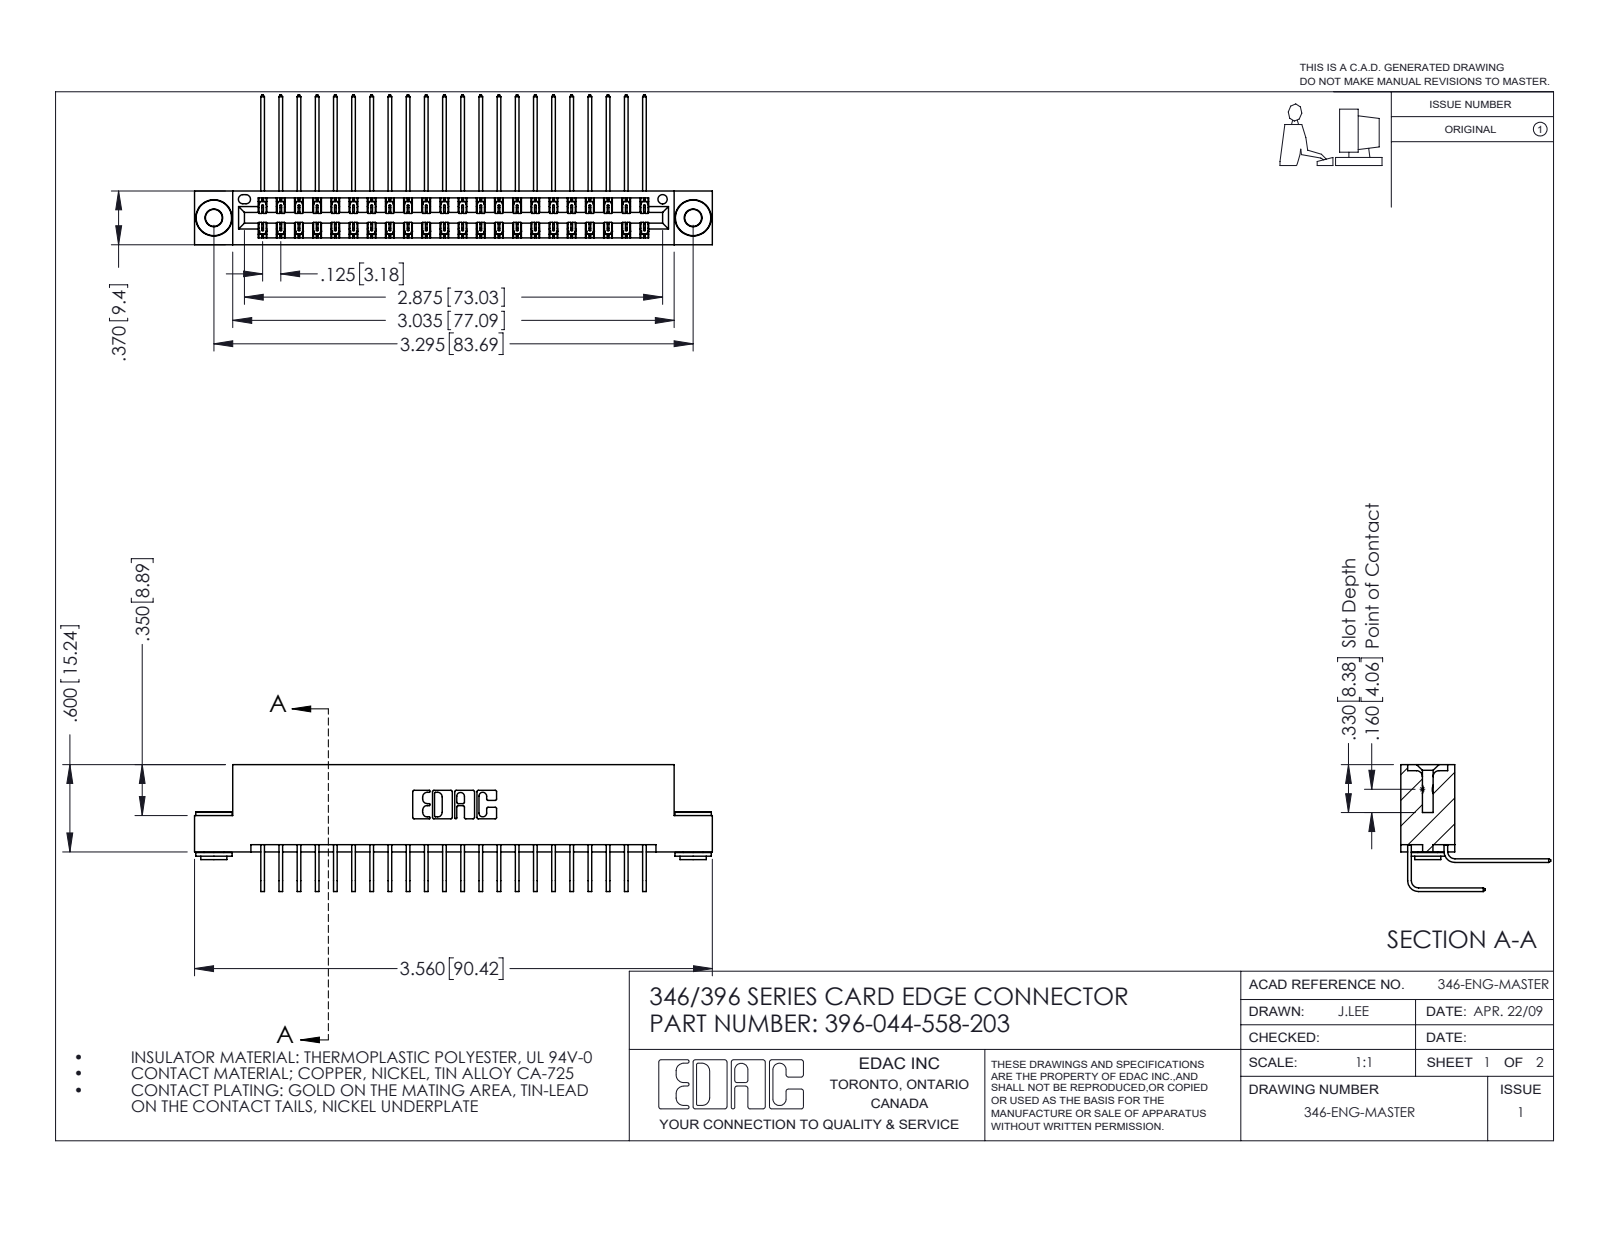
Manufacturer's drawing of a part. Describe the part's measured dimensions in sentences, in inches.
The part is named "345-250-002_345-250-002-102; 346 Part_Flush Mounting Lugs - 0.156 Dia-TH; 396-044-558-203; 345-292-001_558 Tail - 2 (+1 more)". Its 3-D file was written by "SolidWorks 2016 (CONFIG_CONTROL_DESIGN)". It is 47 solids with 2536 faces: 1714 planar, 814 cylindrical and 8 other. Overall it measures 3.56 by 1.03 by 0.873 inches. Its volume is 0.545 cubic inches and its surface area 20.77 square inches. Round holes: 2 of diameter 0.116, 2 of diameter 0.156, 1 of diameter 0.064. Round bosses or shafts: 2 of diameter 0.25, 2 of diameter 0.18, 2 of diameter 0.136. Partial cylindrical surfaces (rounded edges, fillets, slot ends): 66 of radius 0.006, 22 of radius 0.01, 6 of radius 0.007, 6 of radius 0.031, 3 of radius 0.026, 2 of radius 0.014, 2 of radius 0.022, 2 of radius 0.024. The main face-to-face distances are 0.322, 0.048, 0.25, 0.025, 0.37, 0.298, 0.072, 0.275, 0.148, 0.222. The hole center spacings are 0.246, 3.087, 3.295.
